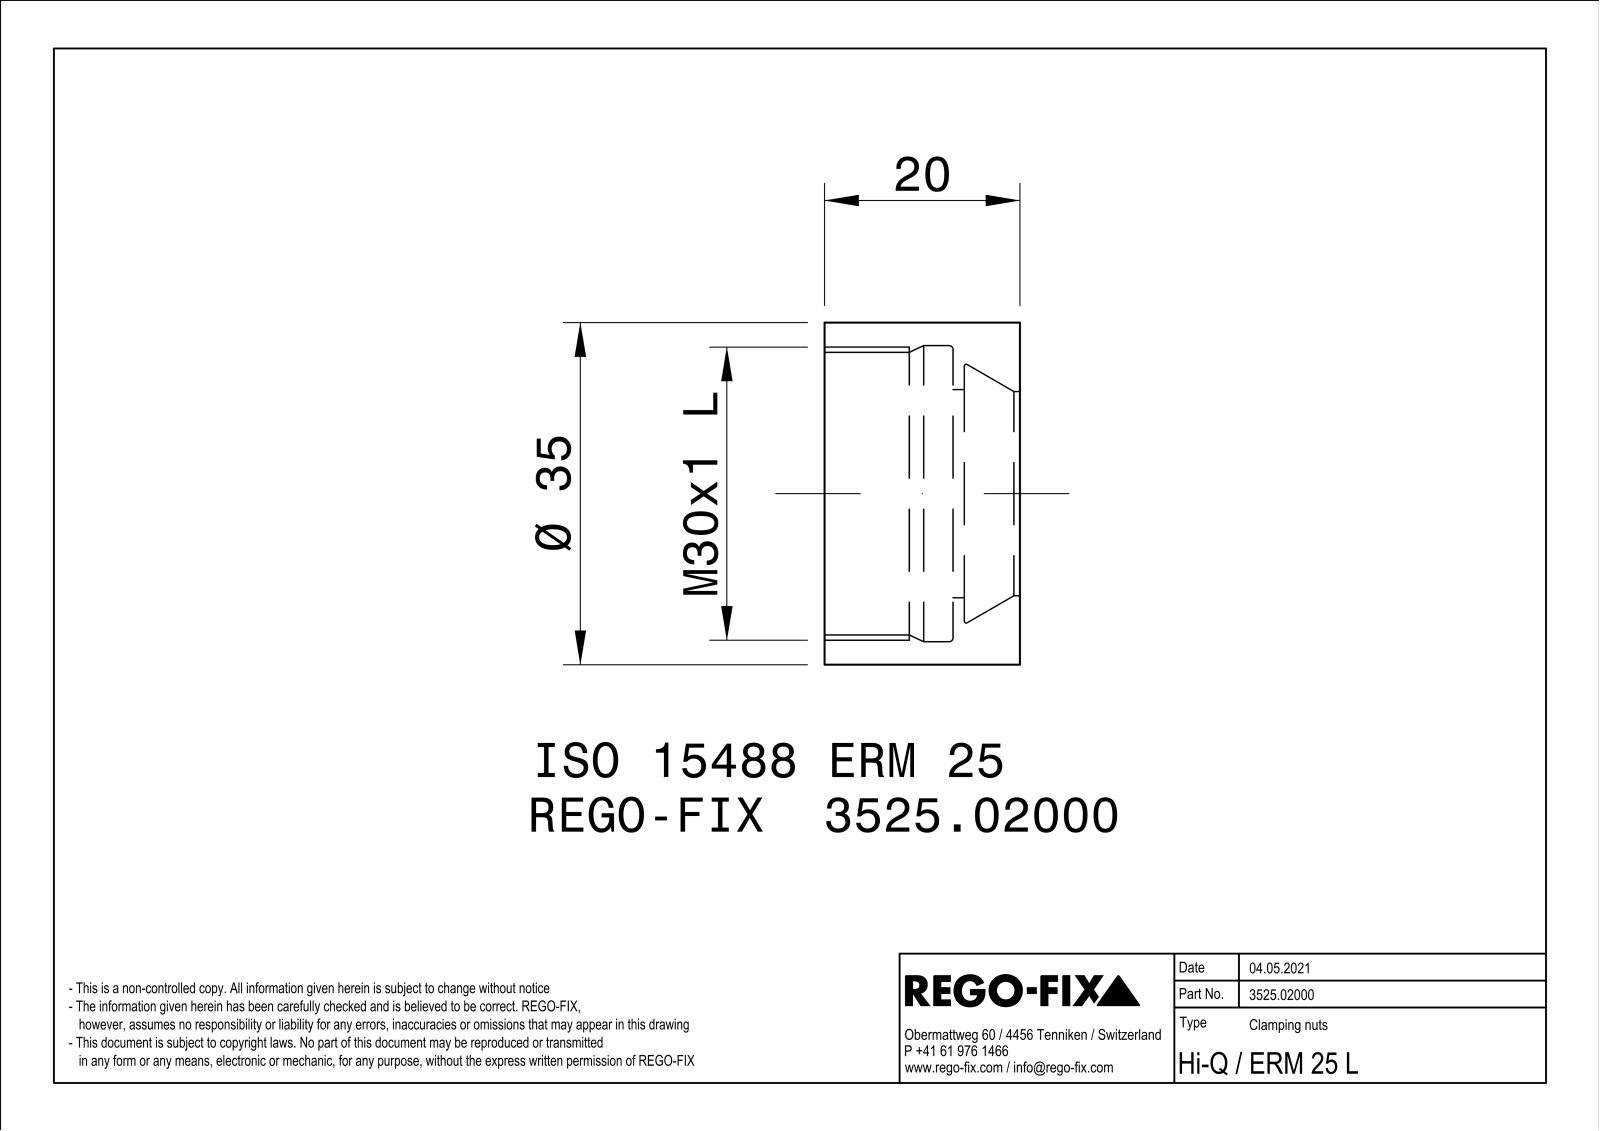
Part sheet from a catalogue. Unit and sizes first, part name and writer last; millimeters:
Units: millimetres
Overall size (bounding box): 35 × 35 × 20
Round holes (diameter × count): ⌀20.9 ×1, ⌀26 ×1, ⌀28.92 ×1, ⌀30.3 ×1
Round bosses / shafts (diameter × count): ⌀35 ×1
Main face-to-face distances: 20, 6.85, 13.15, 5, 5.7, 1.15, 14.3
Volume: 6 891 mm³ · Surface area: 5 105 mm²
Bodies: 1 solid, 38 faces (22 planar, 5 cylindrical, 11 other)
Part name (STEP PRODUCT): NOCUT
STEP written by: SIEMENS PLM Software Solid Edge ST10 (AUTOMOTIVE_DESIGN)
